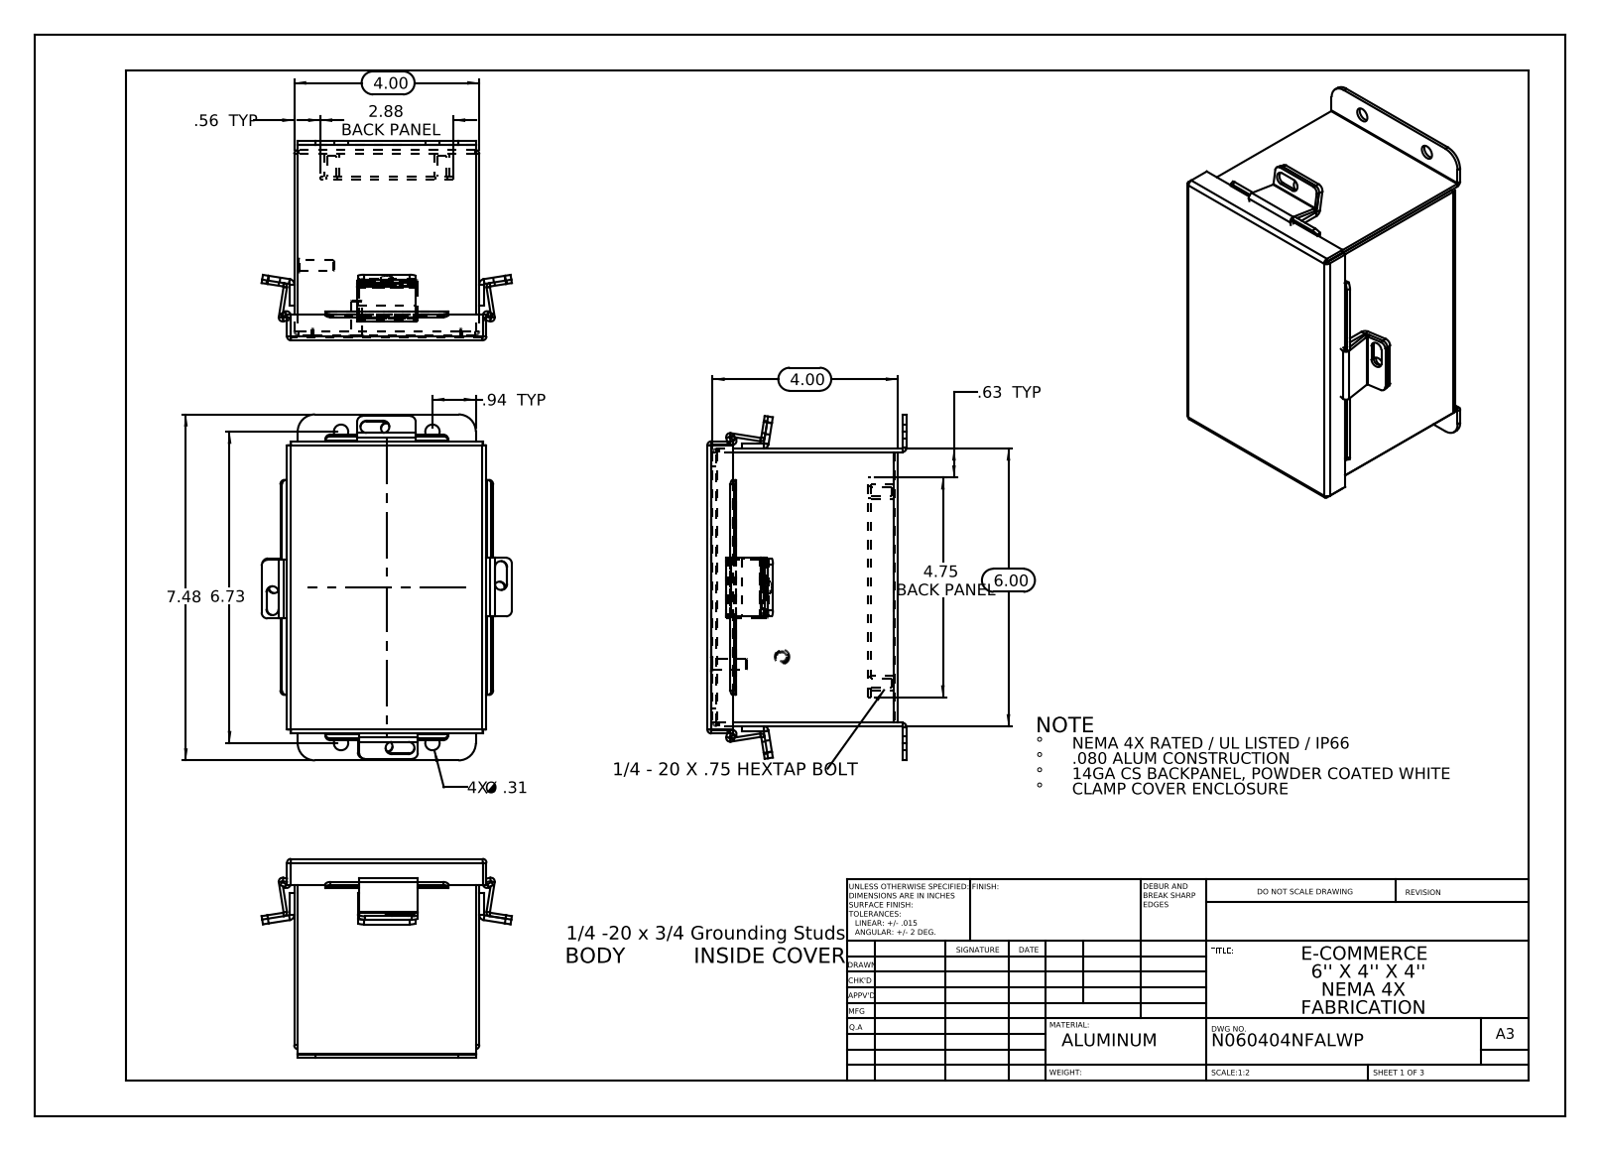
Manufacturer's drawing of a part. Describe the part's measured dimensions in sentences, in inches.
The part is named "N060404NFSSWP JIC Backpanel; N060404NFSSWP JIC Clamp Bracket; N060404NFSSWP JIC Enclosure Template; N060404NFSSWP JIC_Standoff (+6 more)". Its 3-D file was written by "SolidWorks 2013 (CONFIG_CONTROL_DESIGN)". It is 19 solids with 456 faces: 292 planar, 144 cylindrical and 20 other. Overall it measures 7.476 by 5.407 by 4.302 inches. Its volume is 13.51 cubic inches and its surface area 371.1 square inches. Round holes: 8 of diameter 0.25, 4 of diameter 0.187, 4 of diameter 0.312. Round bosses or shafts: 4 of diameter 0.313, 2 of diameter 0.315, 2 of diameter 0.236. Partial cylindrical surfaces (rounded edges, fillets, slot ends): 16 of radius 0.009, 14 of radius 0.125, 12 of radius 0.013, 12 of radius 0.088, 8 of radius 0.083, 8 of radius 0.1, 8 of radius 0.133, 4 of radius 0.084. The main face-to-face distances are 0.075, 3.925, 4.041, 5.925, 3.85, 4, 3.966, 4.115, 0.156, 5.85. The hole center spacings are 1.315, 2.534, 5.43, 5.846, 1.976, 2.375, 4.126, 4.761.
